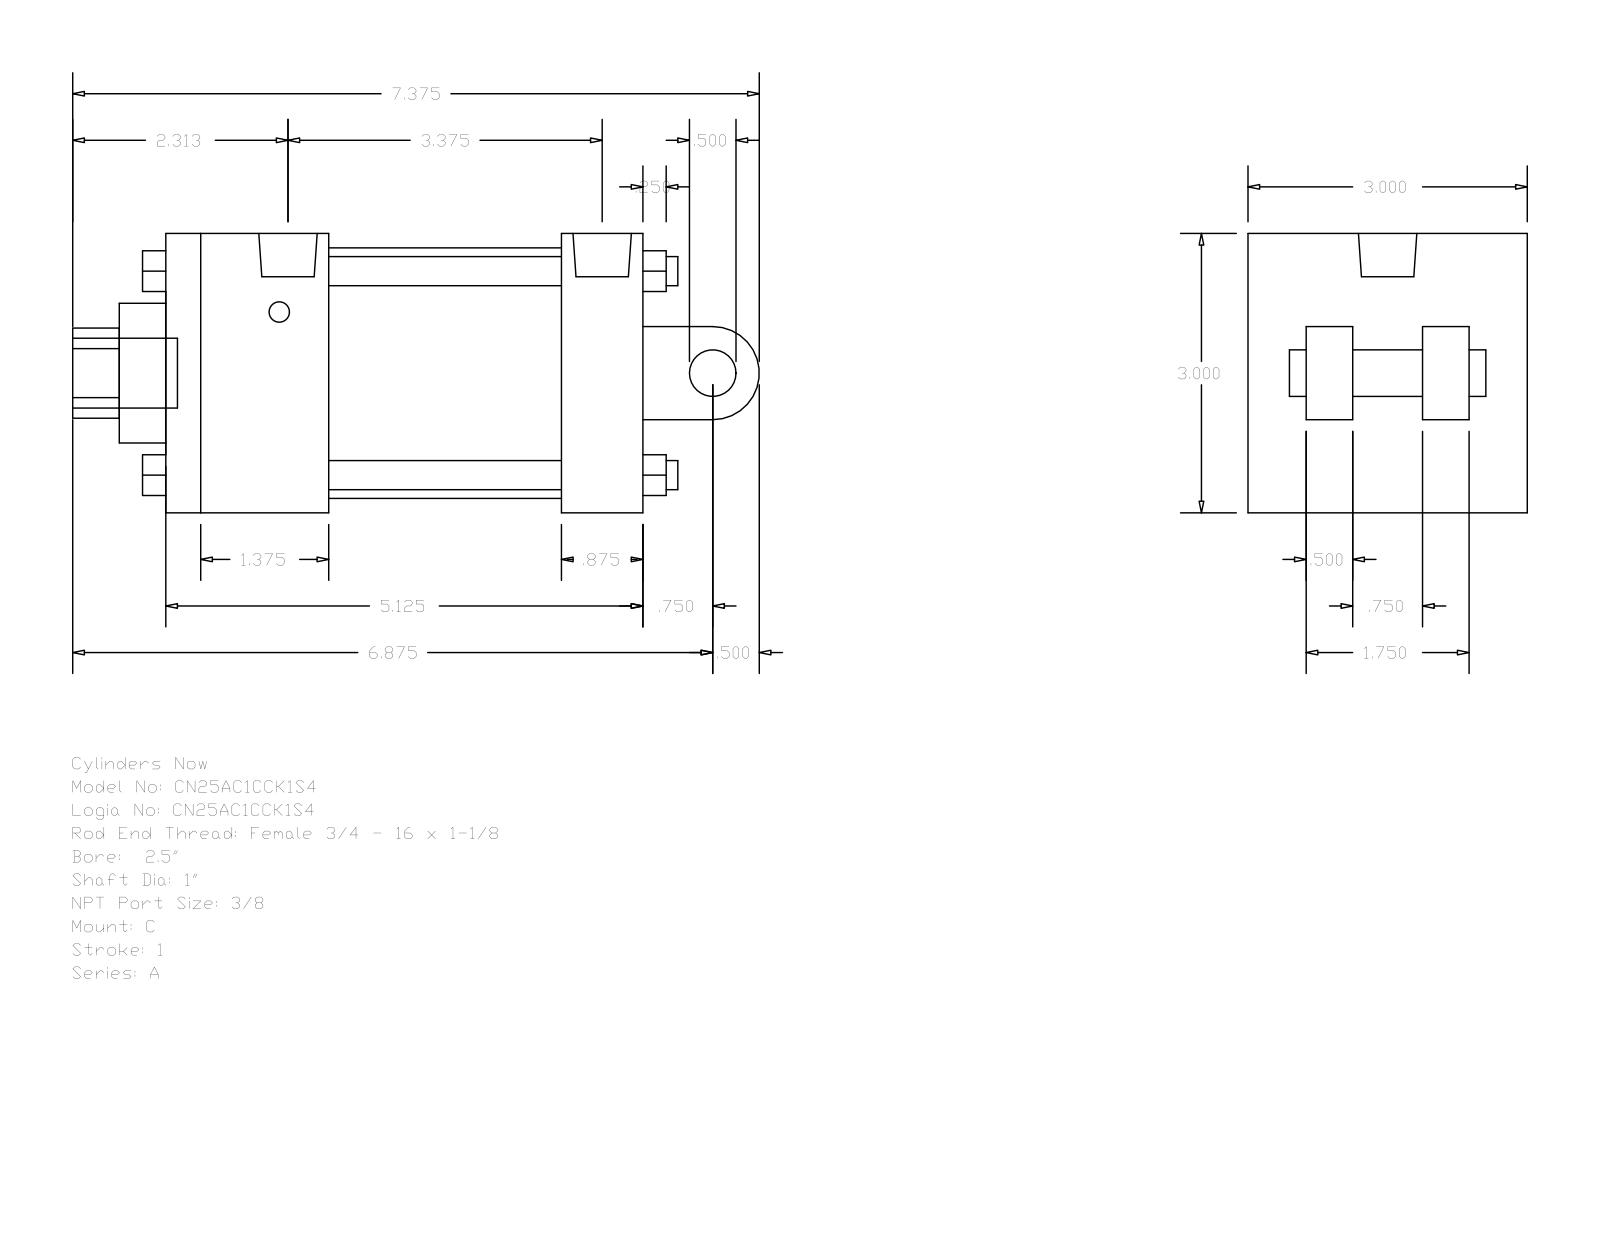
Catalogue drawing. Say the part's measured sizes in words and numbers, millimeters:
The part is named "A_C__0250_1". Its 3-D file was written by "GSSL Pune (CONFIG_CONTROL_DESIGN)". It is 0 solids with 135 faces: 102 planar, 33 cylindrical and 0 other. Overall it measures 187.32 by 76.2 by 76.2 millimeters. Round holes: 2 of diameter 5.56, 1 of diameter 15.93, 1 of diameter 25.4, 1 of diameter 38.1, 1 of diameter 68.33. Round bosses or shafts: 4 of diameter 7.94, 2 of diameter 5.56, 1 of diameter 19.05, 1 of diameter 15.93, 1 of diameter 12.7. Partial cylindrical surfaces (rounded edges, fillets, slot ends): 1 of radius 12.29, 1 of radius 12.7. The main face-to-face distances are 76.2, 130.17, 12.7, 63.5, 44.45, 107.95, 85.72, 22.22, 15.87, 25.4. The hole center spacings are 2.38.
